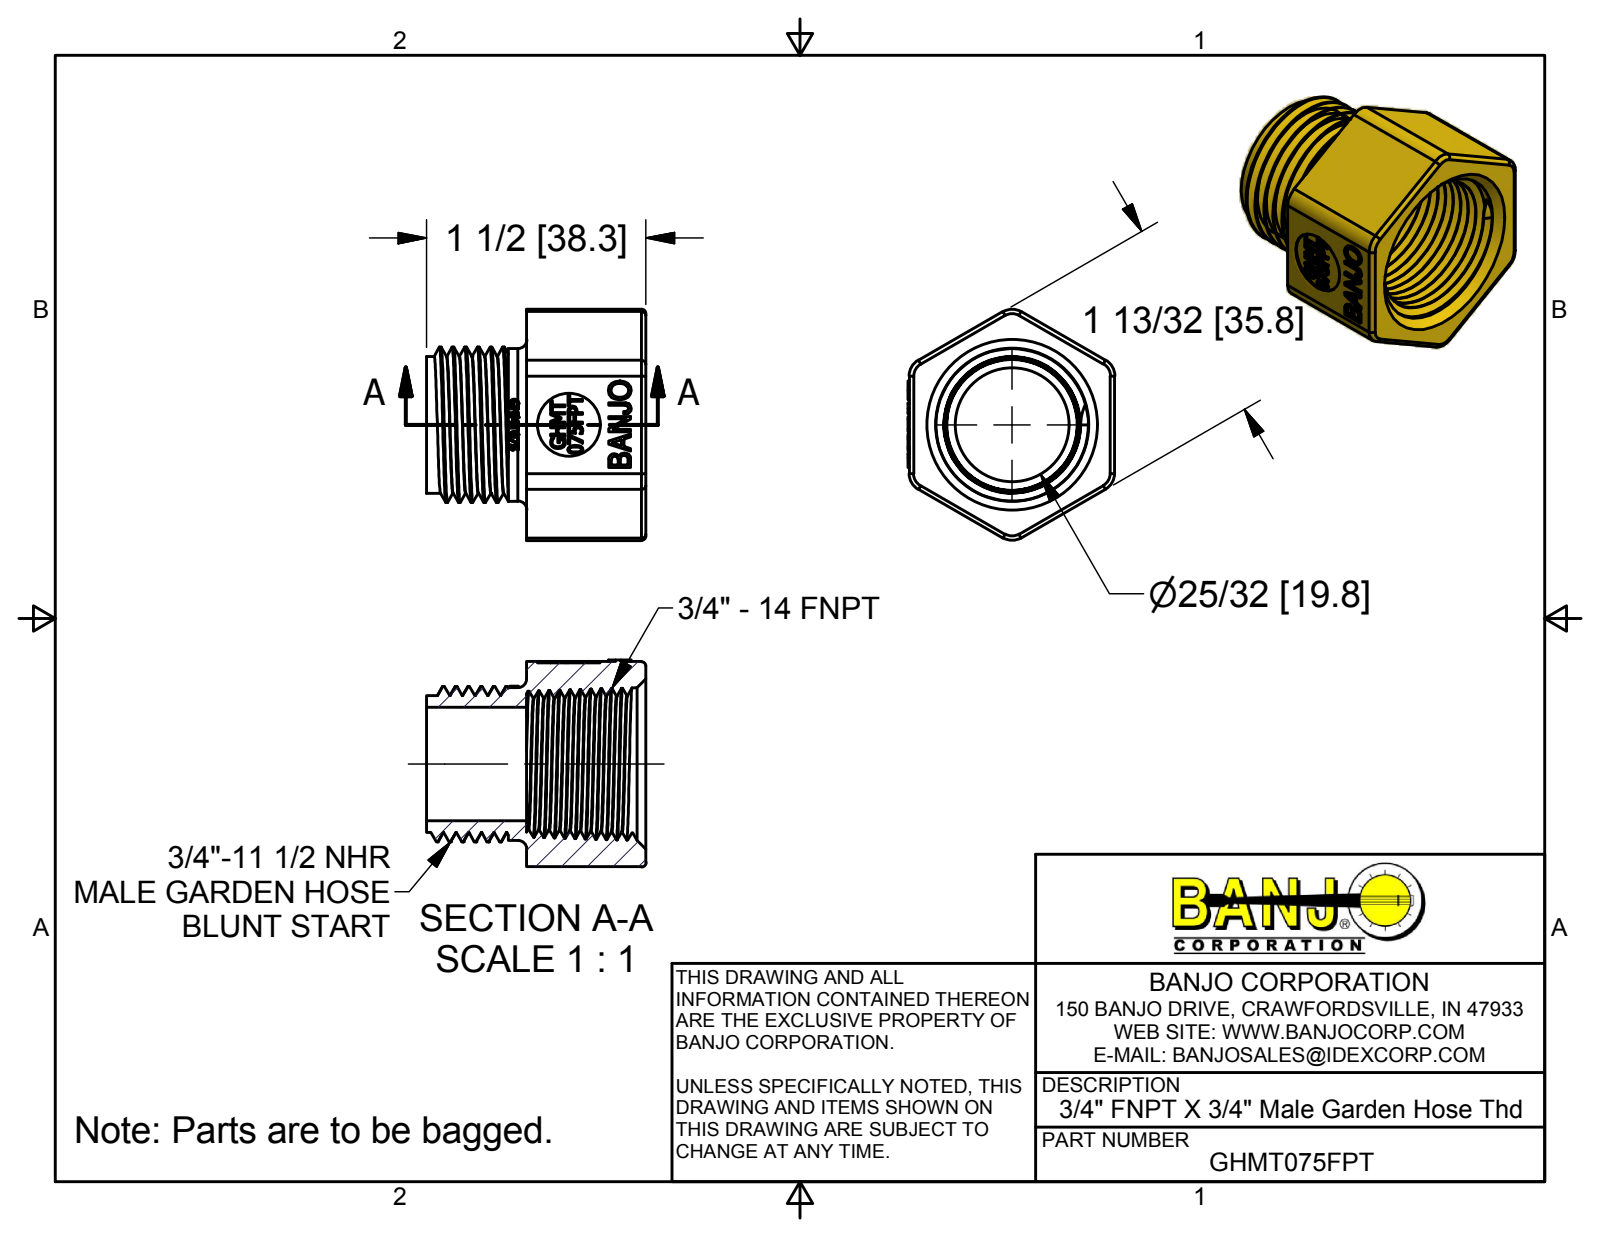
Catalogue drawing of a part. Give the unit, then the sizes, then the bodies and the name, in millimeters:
Units: millimetres
Overall size (bounding box): 40.4 × 38.29 × 36.09
Round holes (diameter × count): ⌀10.92 ×1, ⌀19.81 ×1
Round bosses / shafts (diameter × count): ⌀27.12 ×1, ⌀26.67 ×1, ⌀23.88 ×1
Partial cylindrical surfaces — rounded edges, fillets, slot ends (radius × count): R0.76 ×6, R3.17 ×6, R7.59 ×1, R8.04 ×1, R13.59 ×1
Main face-to-face distances: 35.84, 20.83, 38.29, 17.46, 35.59, 24, 3.17, 14.29, 0.5, 36.09
Volume: 16 476 mm³ · Surface area: 10 102 mm²
Bodies: 1 solid, 373 faces (198 planar, 35 cylindrical, 140 other)
Part name (STEP PRODUCT): GHMT075FPTZ; GHMT075FPT
STEP written by: Autodesk Inventor 2015 (AUTOMOTIVE_DESIGN)
